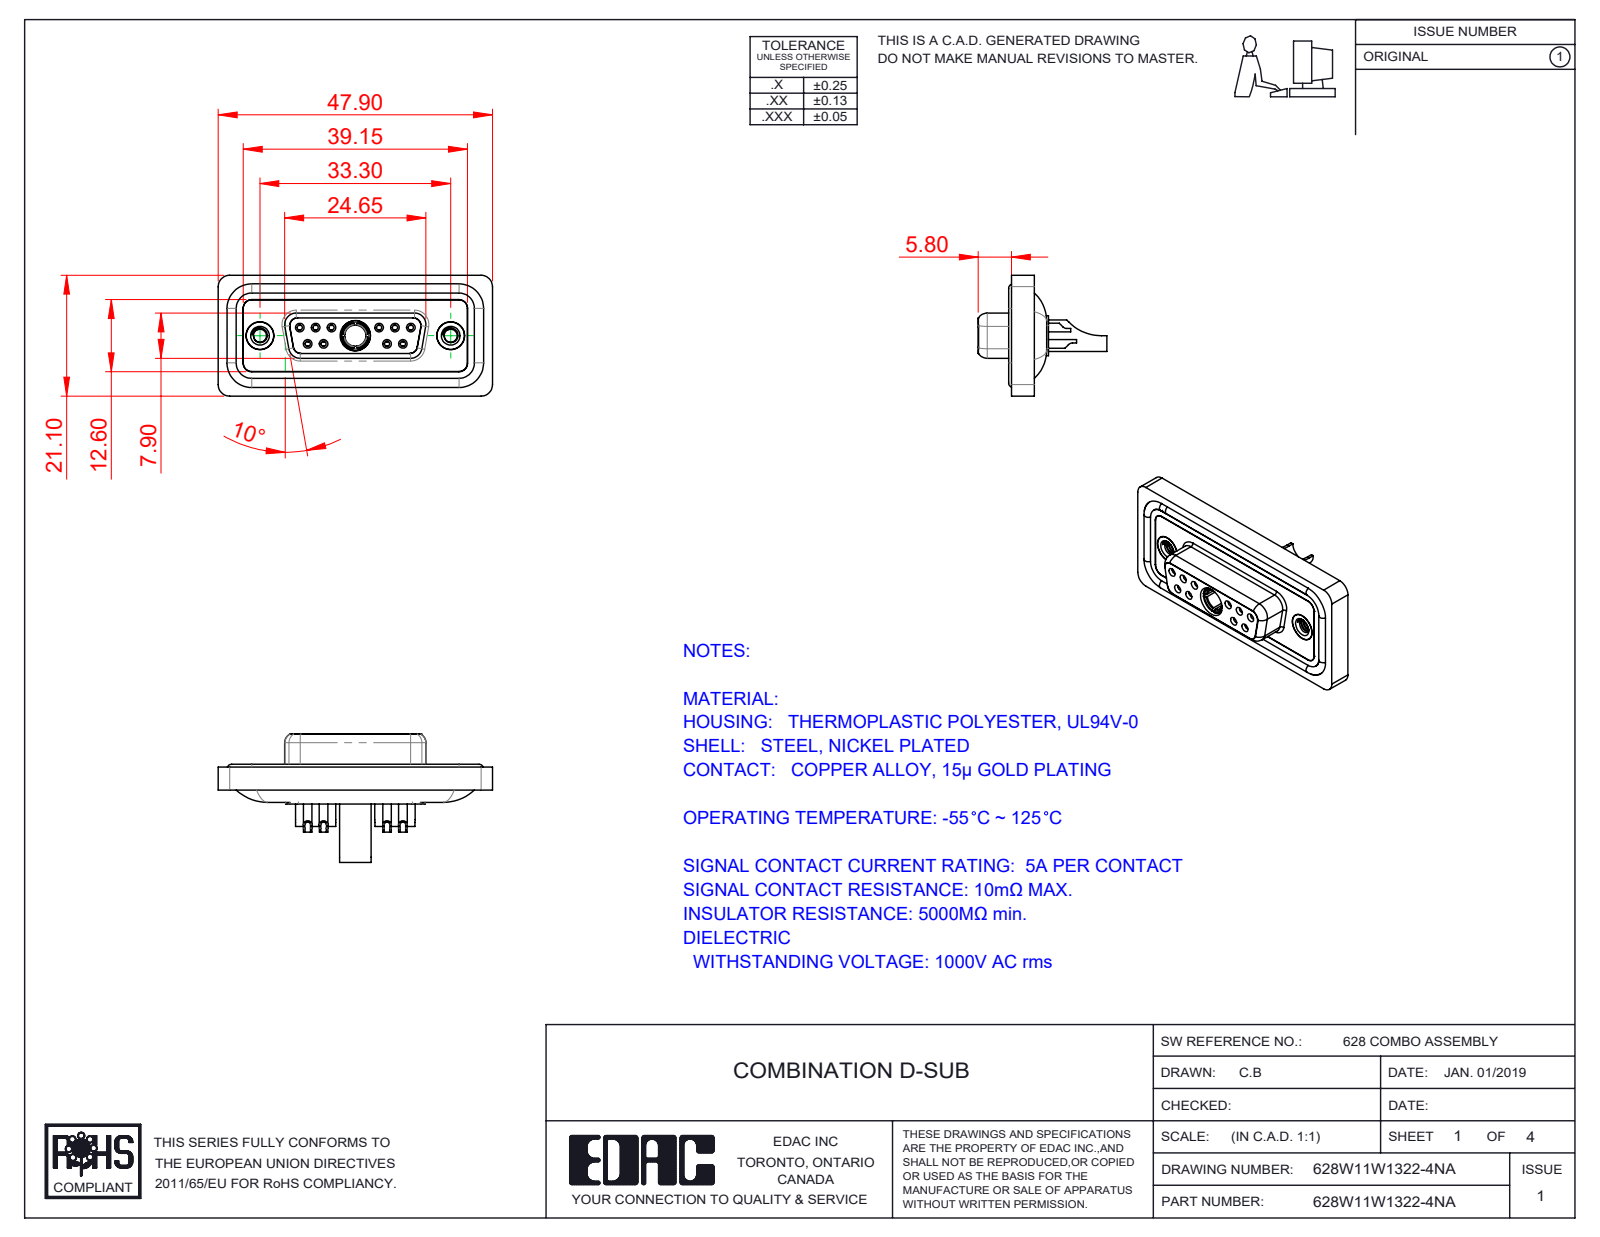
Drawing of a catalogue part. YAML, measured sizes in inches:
part_name: "628Combo Contact Row 2_22; Power Socket_40A SC; 628Combo Shell Front_15 Contacts; 628Combo Housing_11W1 (+5 more)"
step_written_by: "SolidWorks 2023 (CONFIG_CONTROL_DESIGN)"
units: inches
bodies: {solids: 19, faces: 1011, planar: 306, cylindrical: 424, other: 281}
overall_size: [1.886, 0.884, 0.831]
volume: 0.378
surface_area: 15.92
round_holes:
  - {diameter: 0.035, count: 10}
  - {diameter: 0.039, count: 10}
  - {diameter: 0.043, count: 10}
  - {diameter: 0.059, count: 10}
  - {diameter: 0.079, count: 10}
  - {diameter: 0.067, count: 6}
  - {diameter: 0.063, count: 4}
  - {diameter: 0.191, count: 3}
  - {diameter: 0.089, count: 2}
  - {diameter: 0.157, count: 2}
  - {diameter: 0.159, count: 2}
  - {diameter: 0.197, count: 2}
round_bosses_or_shafts:
  - {diameter: 0.087, count: 10}
  - {diameter: 0.063, count: 10}
  - {diameter: 0.195, count: 2}
  - {diameter: 0.189, count: 2}
  - {diameter: 0.217, count: 1}
  - {diameter: 0.205, count: 1}
  - {diameter: 0.195, count: 1}
  - {diameter: 0.187, count: 1}
partial_cylinders:
  - {radius: 0.059, count: 22}
  - {radius: 0.079, count: 20}
  - {radius: 0.053, count: 12}
  - {radius: 0.063, count: 8}
  - {radius: 0.039, count: 6}
  - {radius: 0.01, count: 4}
  - {radius: 0.02, count: 4}
  - {radius: 0.024, count: 4}
face_to_face_distances: [0.016, 0.063, 0.071, 0.114, 0.02, 0.043, 0.222, 0.293, 0.26, 0.278]
hole_center_spacings: [0.124, 0.109, 0.545, 0.436, 0.654, 0.198, 0.198, 0.218]
